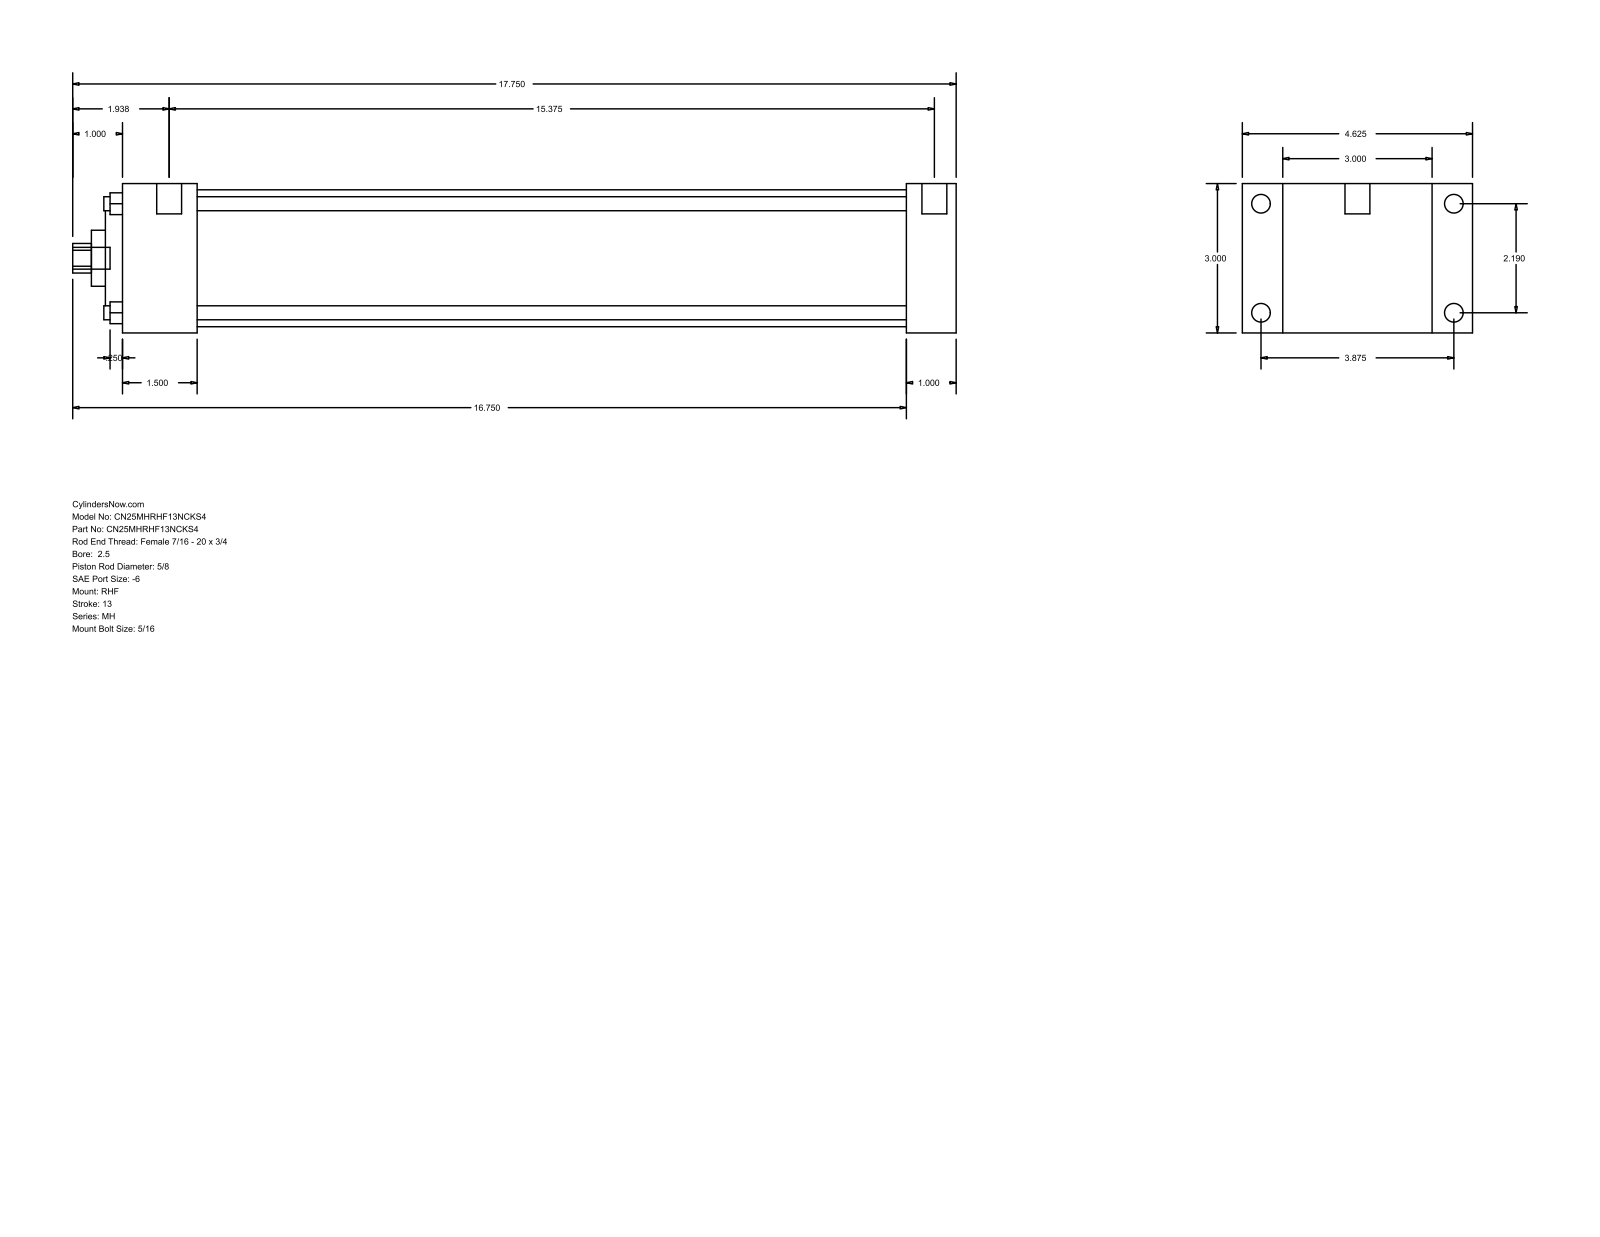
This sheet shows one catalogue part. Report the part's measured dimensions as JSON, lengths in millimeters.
{"part_name": "MH_RHF__0250_0.625", "step_written_by": "GSSL Pune (CONFIG_CONTROL_DESIGN)", "units": "millimeters", "bodies": {"solids": 0, "faces": 90, "planar": 61, "cylindrical": 29, "other": 0}, "overall_size": [450.85, 117.47, 76.2], "round_holes": [[7.14, 4], [15.88, 1], [28.57, 1], [55.55, 1], [69.85, 1]], "round_bosses_or_shafts": [[9.53, 4], [5.56, 4], [12.7, 2], [11.11, 1]], "partial_cylinders_radius": [[7.54, 1]], "face_to_face_distances": [76.2, 25.4, 20.64, 96.84, 425.45, 400.05, 117.48, 38.1, 361.95, 387.35], "hole_center_spacings": [39.33, 55.62, 78.66]}
